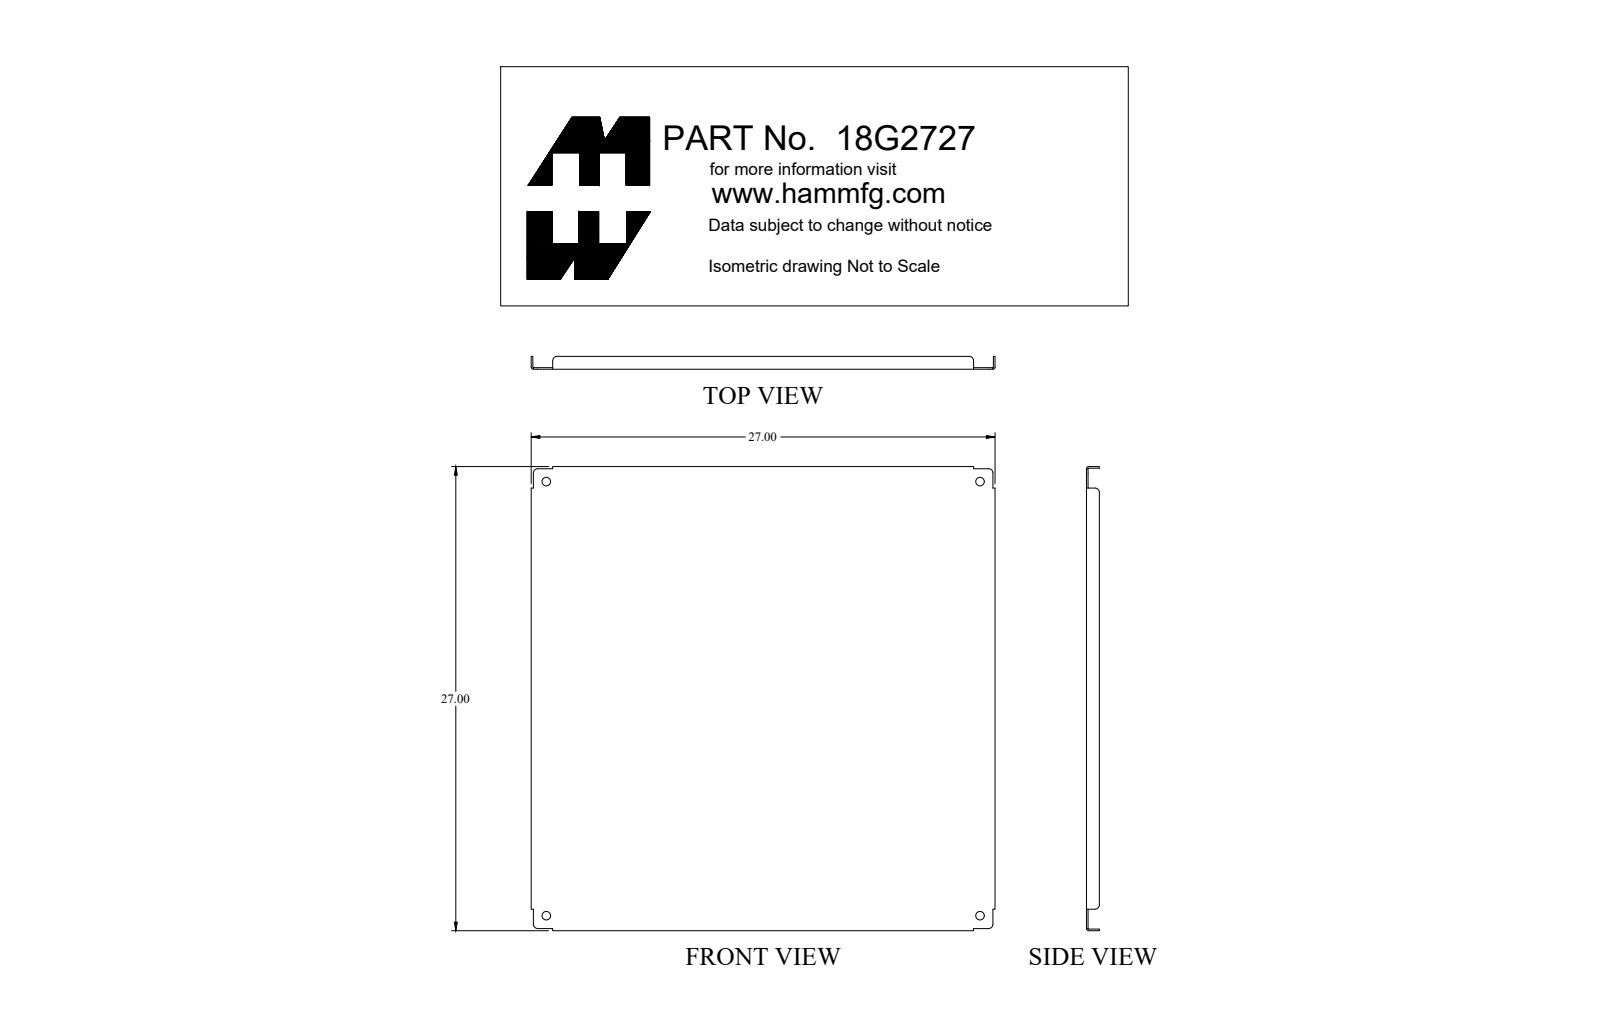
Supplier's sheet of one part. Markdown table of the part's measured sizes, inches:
| quantity | value |
| --- | --- |
| part name | 18G2727 |
| STEP written by | SolidWorks 2018 (AUTOMOTIVE_DESIGN) |
| units | inches |
| bodies | 1 solid, 54 faces (30 planar, 24 cylindrical, 0 other) |
| overall size | 27 × 27 × 0.75 |
| volume | 74.84 in³ |
| surface area | 1 587 in² |
| round holes (diameter × count) | 0.5 × 4 |
| partial cylindrical surfaces (radius × count) | 0.25 × 8, 0.03 × 4, 0.125 × 4 |
| main face-to-face distances | 0.095, 26.905, 26.81, 27, 0.75, 0.655, 0.125, 26.875, 0.03, 26.78 |
| hole center spacings | 25.25, 35.708 |
